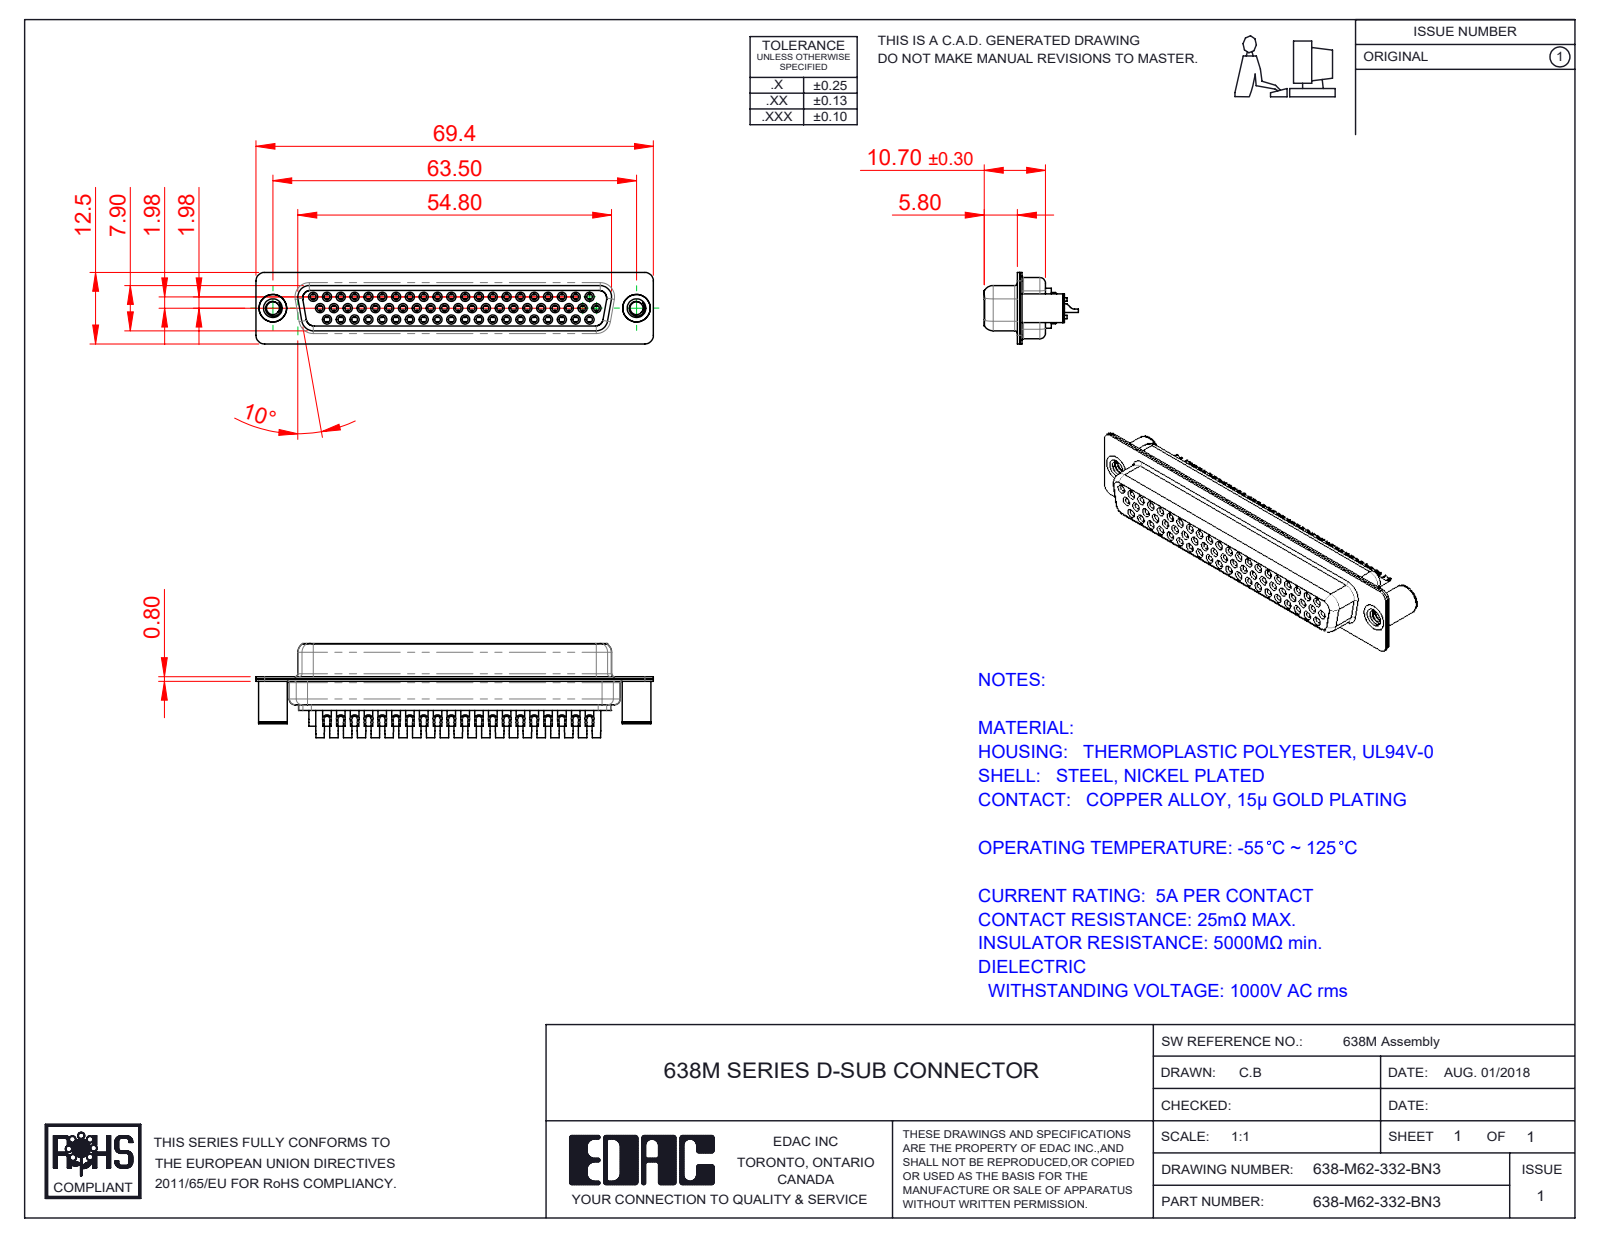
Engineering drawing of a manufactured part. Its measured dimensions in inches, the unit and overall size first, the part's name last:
Units: inches
Overall size (bounding box): 2.732 × 0.648 × 0.492
Round holes (diameter × count): ⌀0.039 ×62, ⌀0.043 ×62, ⌀0.067 ×62, ⌀0.071 ×62, ⌀0.079 ×62, ⌀0.089 ×2, ⌀0.128 ×2, ⌀0.157 ×2, ⌀0.189 ×2
Round bosses / shafts (diameter × count): ⌀0.087 ×62, ⌀0.063 ×62, ⌀0.059 ×62, ⌀0.197 ×2, ⌀0.193 ×2
Partial cylindrical surfaces — rounded edges, fillets, slot ends (radius × count): R0.059 ×16, R0.079 ×12, R0.053 ×8, R0.063 ×8, R0.039 ×7, R0.01 ×4, R0.02 ×4, R0.024 ×4
Main face-to-face distances: 0.016, 0.055, 0.018, 0.333, 0.35, 0.071, 0.039, 0.244, 0.278, 0.073
Hole centre spacings: 0.285, 0.091, 0.095, 0.163, 0.38, 0.19, 0.57, 0.665
Volume: 0.317 in³ · Surface area: 26.55 in²
Bodies: 67 solids, 3723 faces (1121 planar, 1463 cylindrical, 1139 other)
Part name (STEP PRODUCT): 638M Housing_62 Contacts; 638M Contact Row 2_32; 638M Contact Row 1_32; 638M 4-40 Threaded Board Spacer (+4 more)
STEP written by: SolidWorks 2020 (CONFIG_CONTROL_DESIGN)
